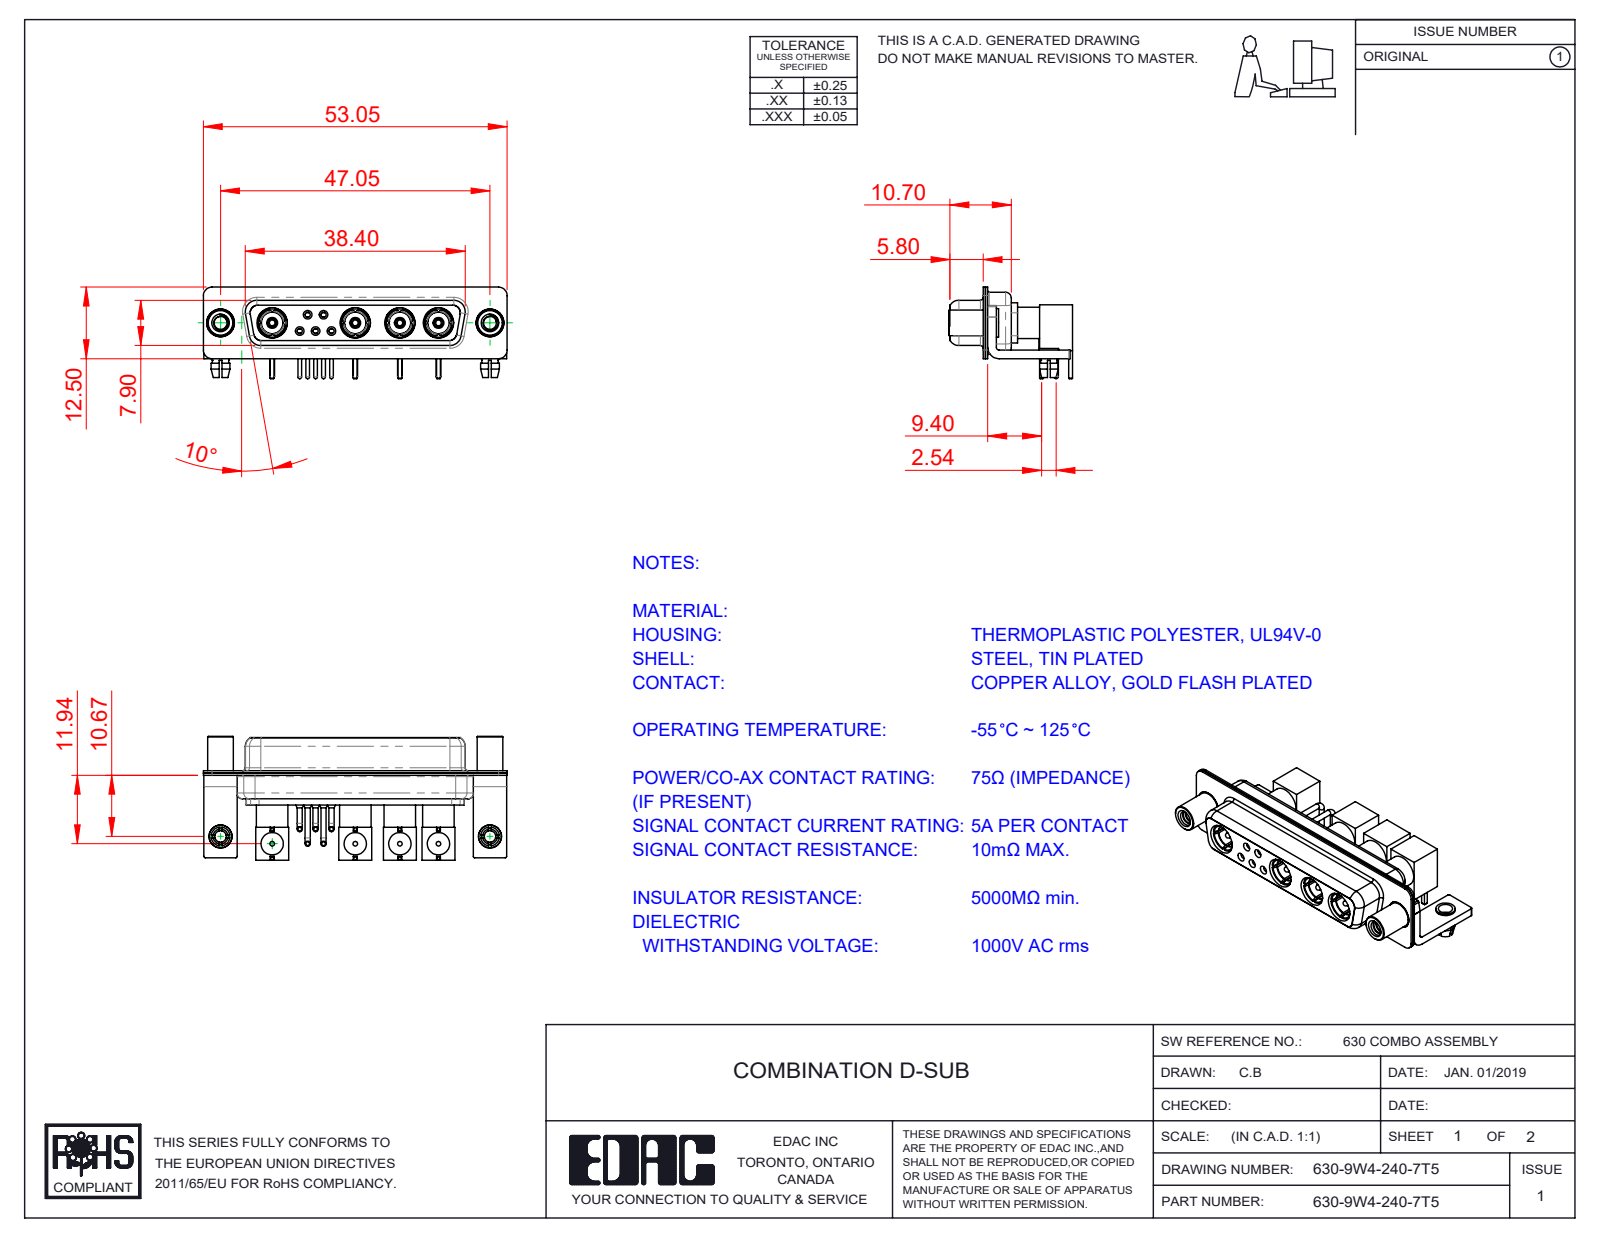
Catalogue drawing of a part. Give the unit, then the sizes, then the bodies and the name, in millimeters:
Units: millimetres
Overall size (bounding box): 53.05 × 21.61 × 16
Round holes (diameter × count): ⌀1.1 ×9, ⌀1.5 ×9, ⌀2 ×7, ⌀4.85 ×6, ⌀0.9 ×5, ⌀0.8 ×4, ⌀2.83 ×4, ⌀3.1 ×4, ⌀3.3 ×4, ⌀3.9 ×4, ⌀3.92 ×4, ⌀4.1 ×4
Round bosses / shafts (diameter × count): ⌀5 ×6, ⌀4 ×6, ⌀2.9 ×6, ⌀0.9 ×5, ⌀0.8 ×5, ⌀0.65 ×5, ⌀5.5 ×4, ⌀5.2 ×4
Partial cylindrical surfaces — rounded edges, fillets, slot ends (radius × count): R0.25 ×16, R1.5 ×16, R2 ×13, R1.35 ×8, R1.6 ×8, R0.5 ×5, R0.6 ×4, R0.65 ×4
Main face-to-face distances: 0.4, 1.4, 1.8, 0.45, 0.8, 8.45, 8.9, 1.35, 1.85, 7.05
Hole centre spacings: 3.16, 6.74, 7.79, 14.51, 14.52, 14.53, 22.3, 29.04
Volume: 5 119 mm³ · Surface area: 12 456 mm²
Bodies: 38 solids, 1396 faces (480 planar, 604 cylindrical, 312 other)
Part name (STEP PRODUCT): 630Combo Housing_9W4; Pin_RA; Insulator RA Pin; 630Combo Shell Front_25 Contacts (+8 more)
STEP written by: SolidWorks 2020 (CONFIG_CONTROL_DESIGN)
